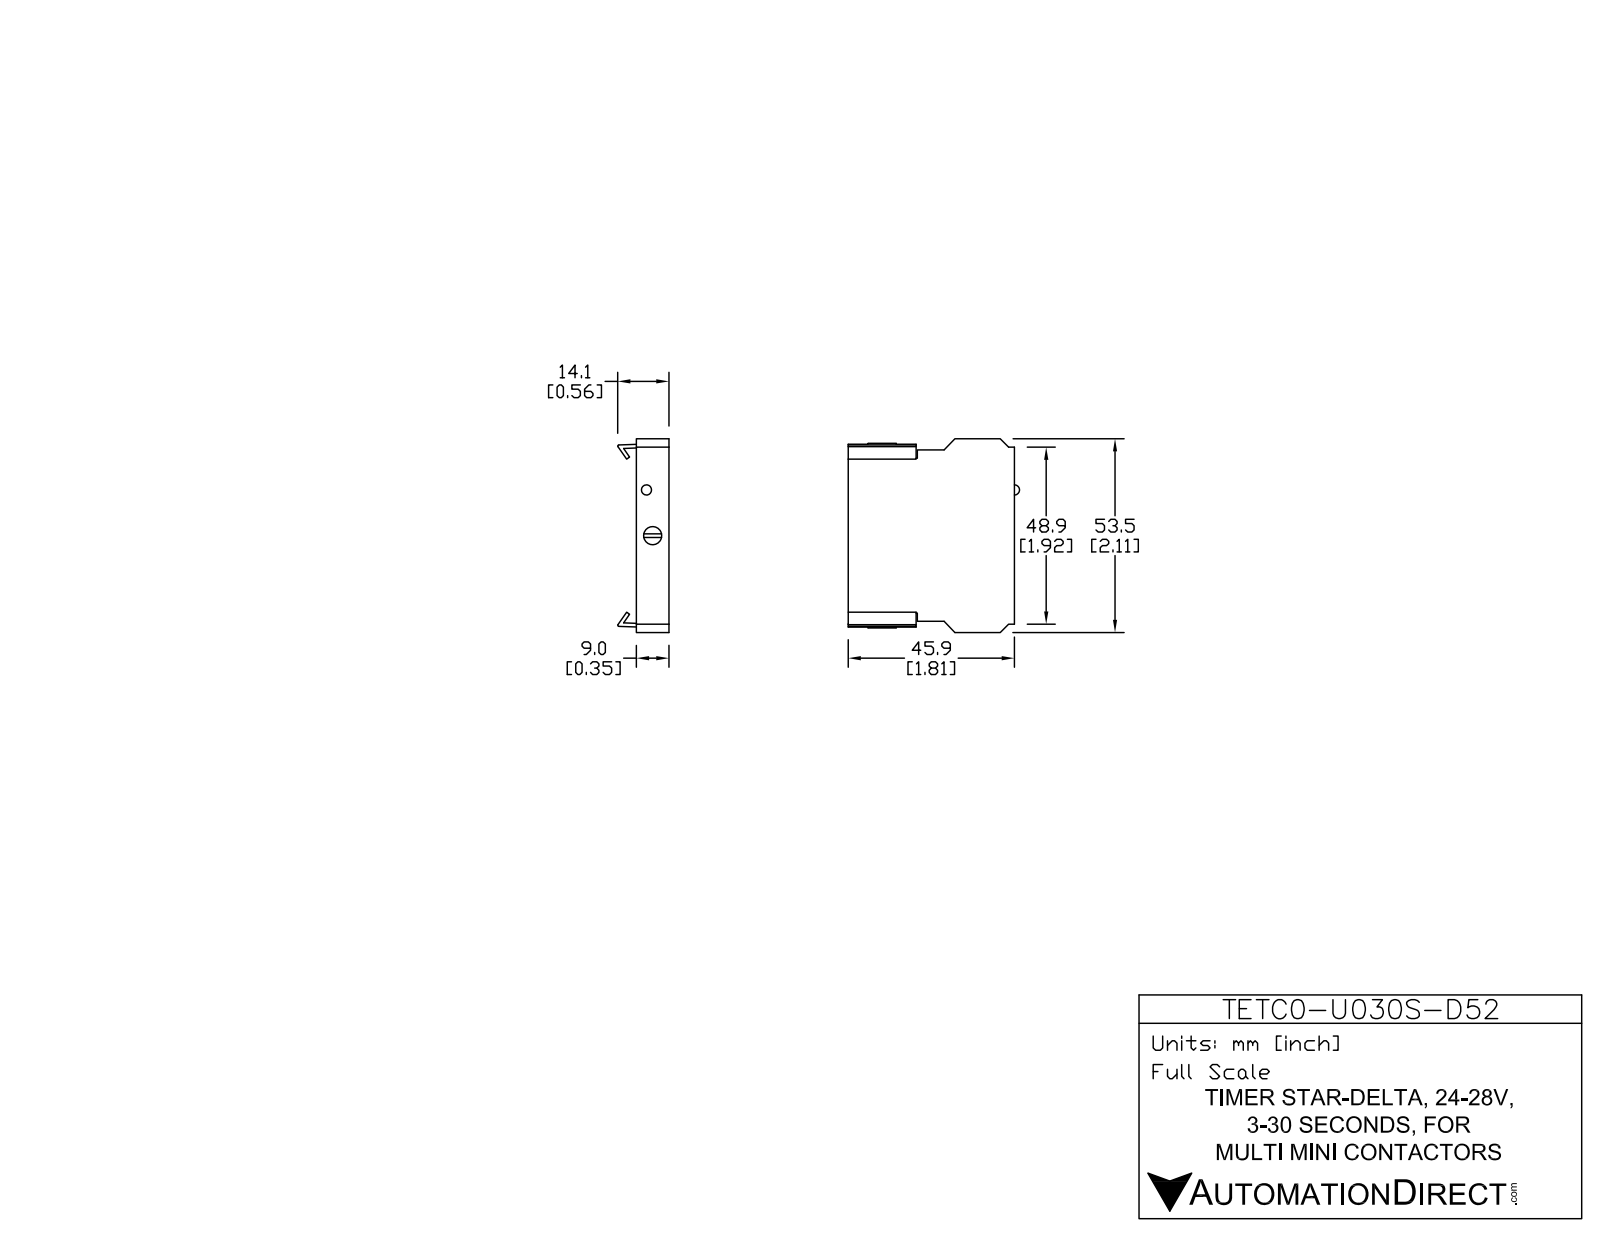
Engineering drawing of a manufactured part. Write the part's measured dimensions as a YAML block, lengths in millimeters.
part_name: "TETC0-U030S-D52"
step_written_by: "SolidWorks 2013 (AUTOMOTIVE_DESIGN)"
units: millimeters
bodies: {solids: 3, faces: 102, planar: 76, cylindrical: 22, other: 4}
overall_size: [53.5, 47.9, 13.54]
volume: 22366
surface_area: 7471
round_holes:
  - {diameter: 0.55, count: 1}
  - {diameter: 3, count: 1}
  - {diameter: 5.5, count: 1}
round_bosses_or_shafts:
  - {diameter: 5.25, count: 1}
partial_cylinders:
  - {radius: 0.3, count: 2}
  - {radius: 0.8, count: 2}
  - {radius: 1, count: 2}
  - {radius: 2, count: 2}
face_to_face_distances: [10, 45.9, 1, 5.32, 48.18, 3.1, 50.4, 2.22, 45.08, 42.86]
hole_center_spacings: [1.85, 12.26, 14.07]
